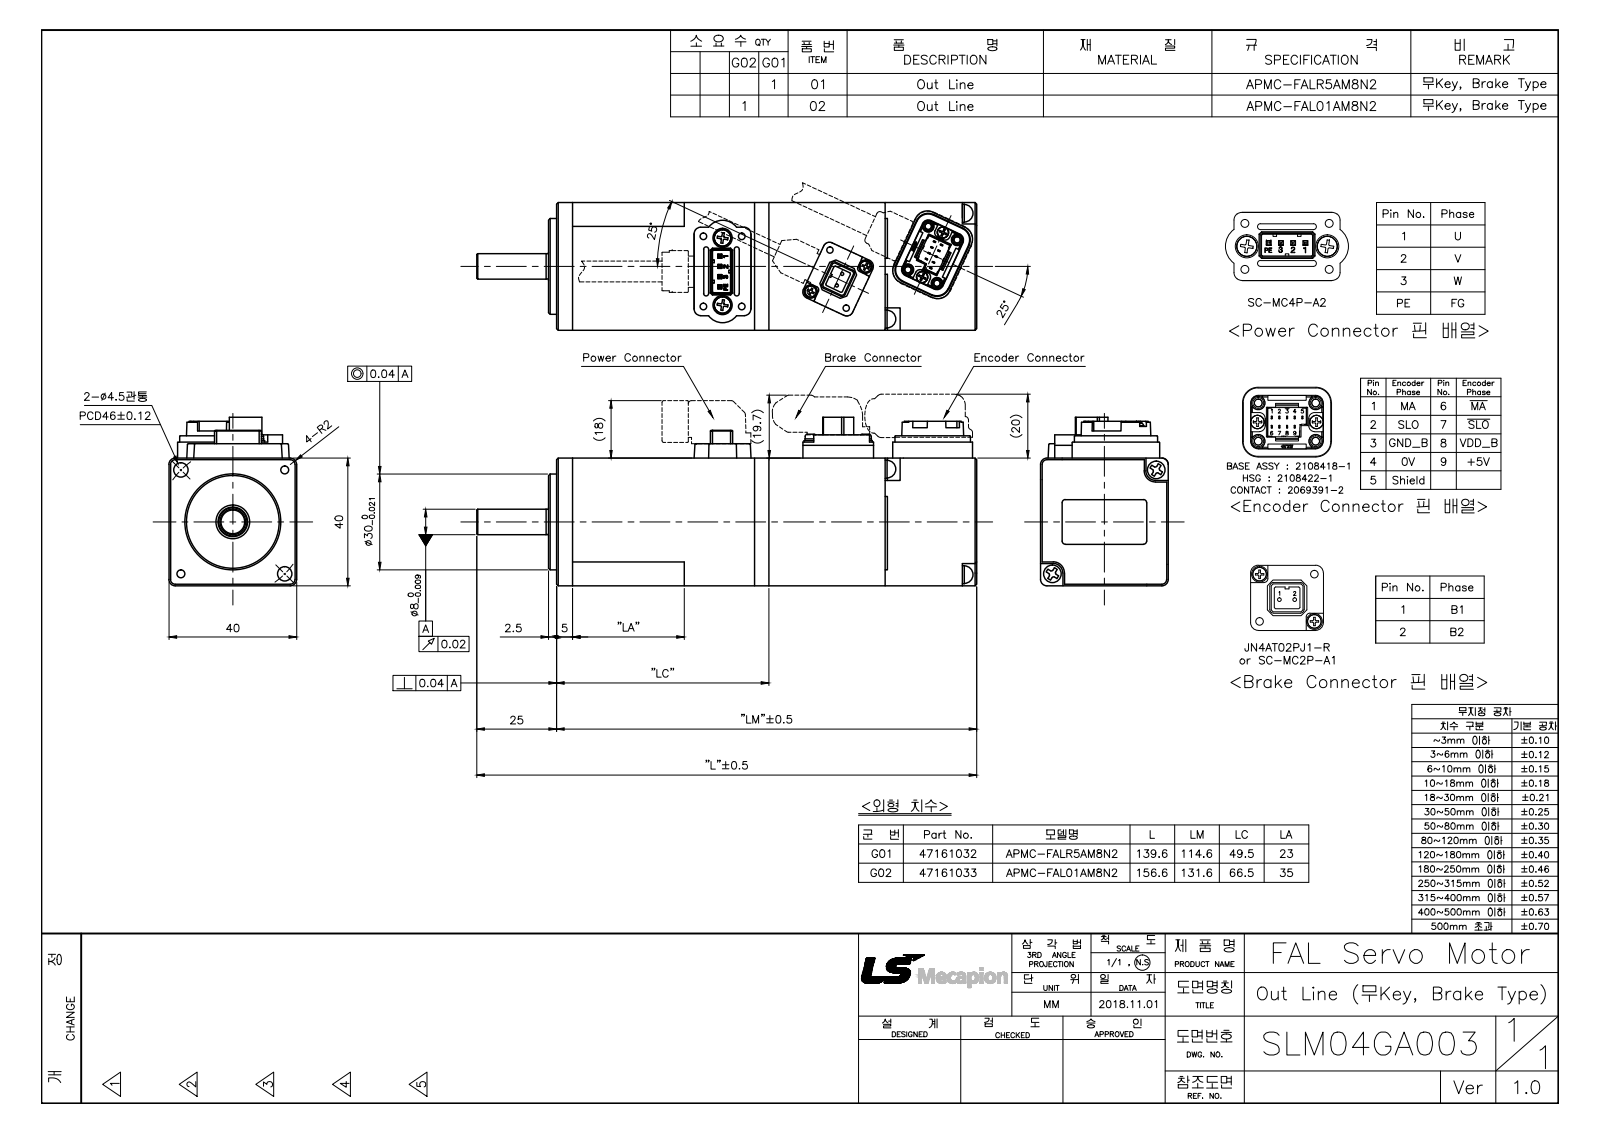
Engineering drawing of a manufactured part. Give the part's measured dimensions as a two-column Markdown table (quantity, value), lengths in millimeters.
| quantity | value |
| --- | --- |
| part name | APMC-FAL01AM8N2 |
| STEP written by | SolidWorks 2011 (AUTOMOTIVE_DESIGN) |
| units | millimeters |
| bodies | 33 solids, 1508 faces (980 planar, 346 cylindrical, 182 other) |
| overall size | 156.6 × 52.8 × 40 |
| volume | 215 302 mm³ |
| surface area | 55 053 mm² |
| round holes (diameter × count) | 2.1 × 10, 2 × 6, 3 × 6, 3.6 × 4, 1 × 2, 2.2 × 2, 2.5 × 2, 4.5 × 2, 6 × 2, 3.3 × 1, 3.4 × 1, 10.6 × 1 |
| round bosses / shafts (diameter × count) | 5.4 × 6, 4.2 × 2, 3.6 × 2, 3.5 × 2, 0.9 × 2, 30 × 1, 9.8 × 1, 9.5 × 1 |
| partial cylindrical surfaces (radius × count) | 0.2 × 20, 1 × 10, 0.15 × 9, 2 × 8, 0.45 × 7, 0.11 × 6, 1.5 × 6, 0.3 × 4 |
| main face-to-face distances | 40, 4.5, 40.9, 0.7, 36.4, 97.9, 61.5, 57, 37.1, 41.6 |
| hole center spacings | 6.02, 9.43, 16, 22.32, 23, 32.52, 2.06, 5 |
